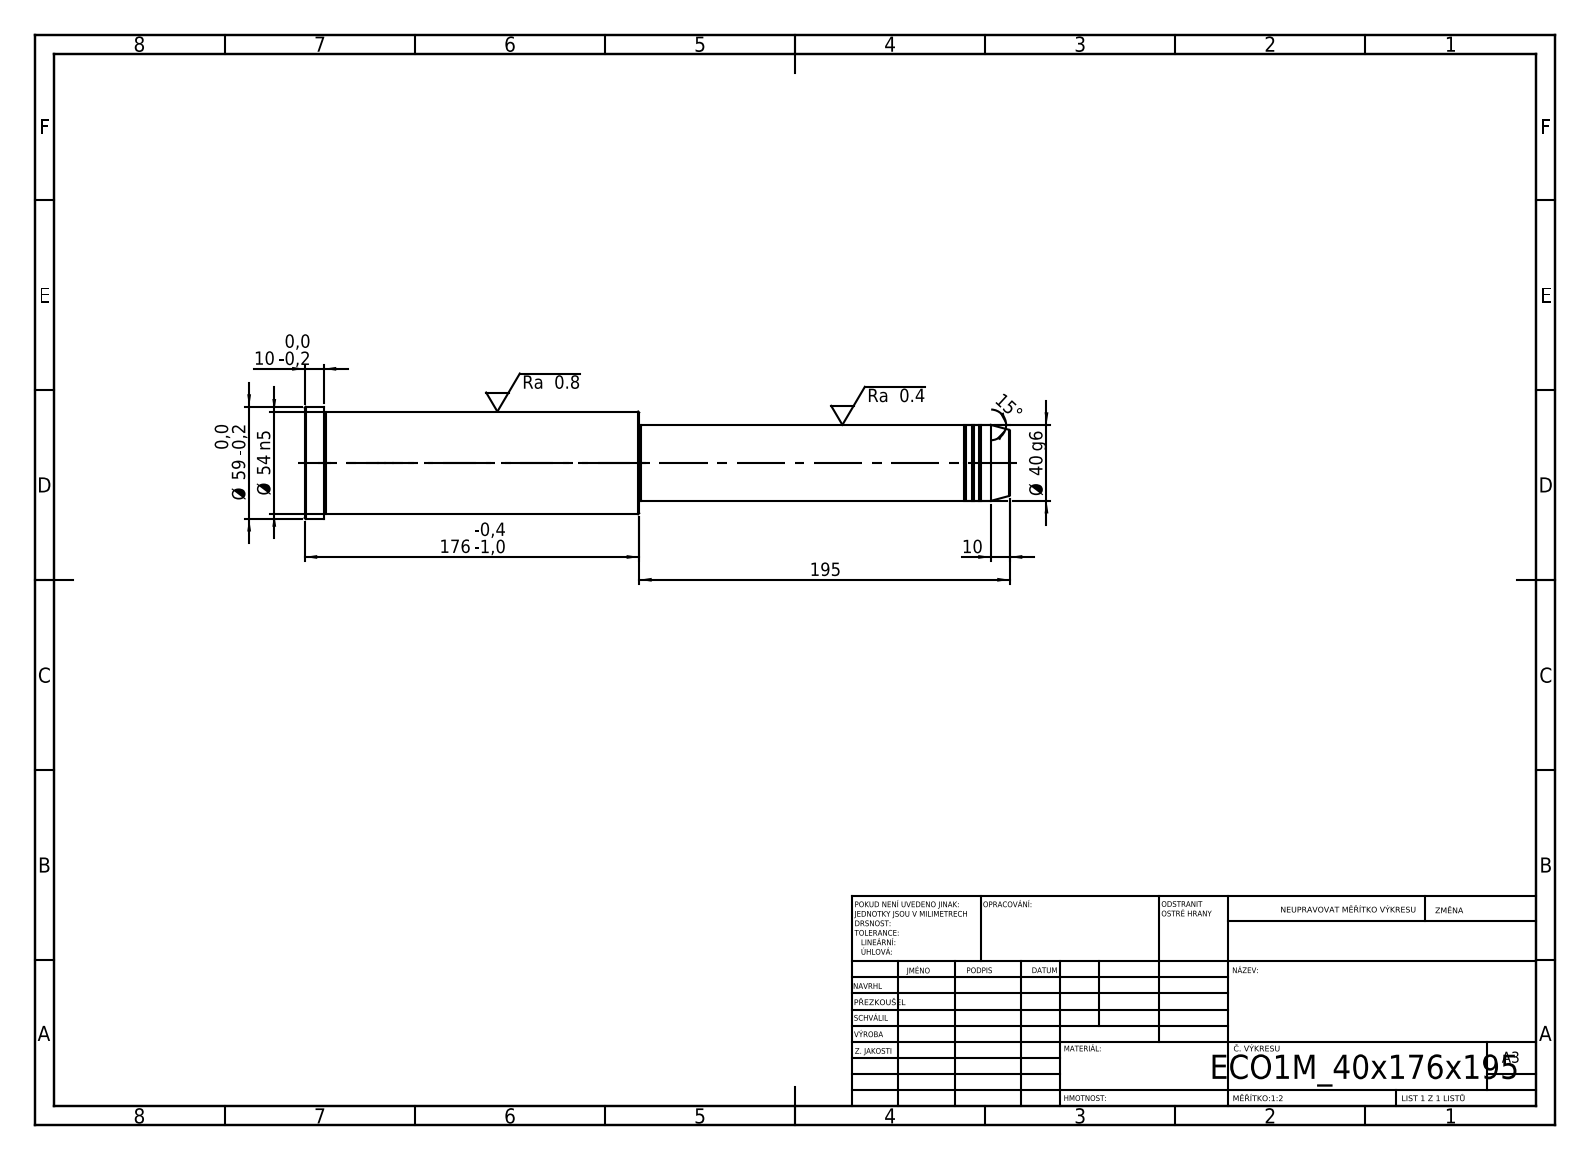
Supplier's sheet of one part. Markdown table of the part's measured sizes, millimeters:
| quantity | value |
| --- | --- |
| STEP written by | SolidWorks 2019 (CONFIG_CONTROL_DESIGN) |
| units | millimeters |
| bodies | 1 solid, 43 faces (5 planar, 14 cylindrical, 24 other) |
| overall size | 371 × 59 × 59 |
| volume | 650 630 mm³ |
| surface area | 59 934 mm² |
| round bosses / shafts (diameter × count) | 59 × 1, 54 × 1, 40 × 1, 39 × 1 |
| main face-to-face distances | 176, 195, 371, 361, 166, 10, 194, 1, 167, 177 |
